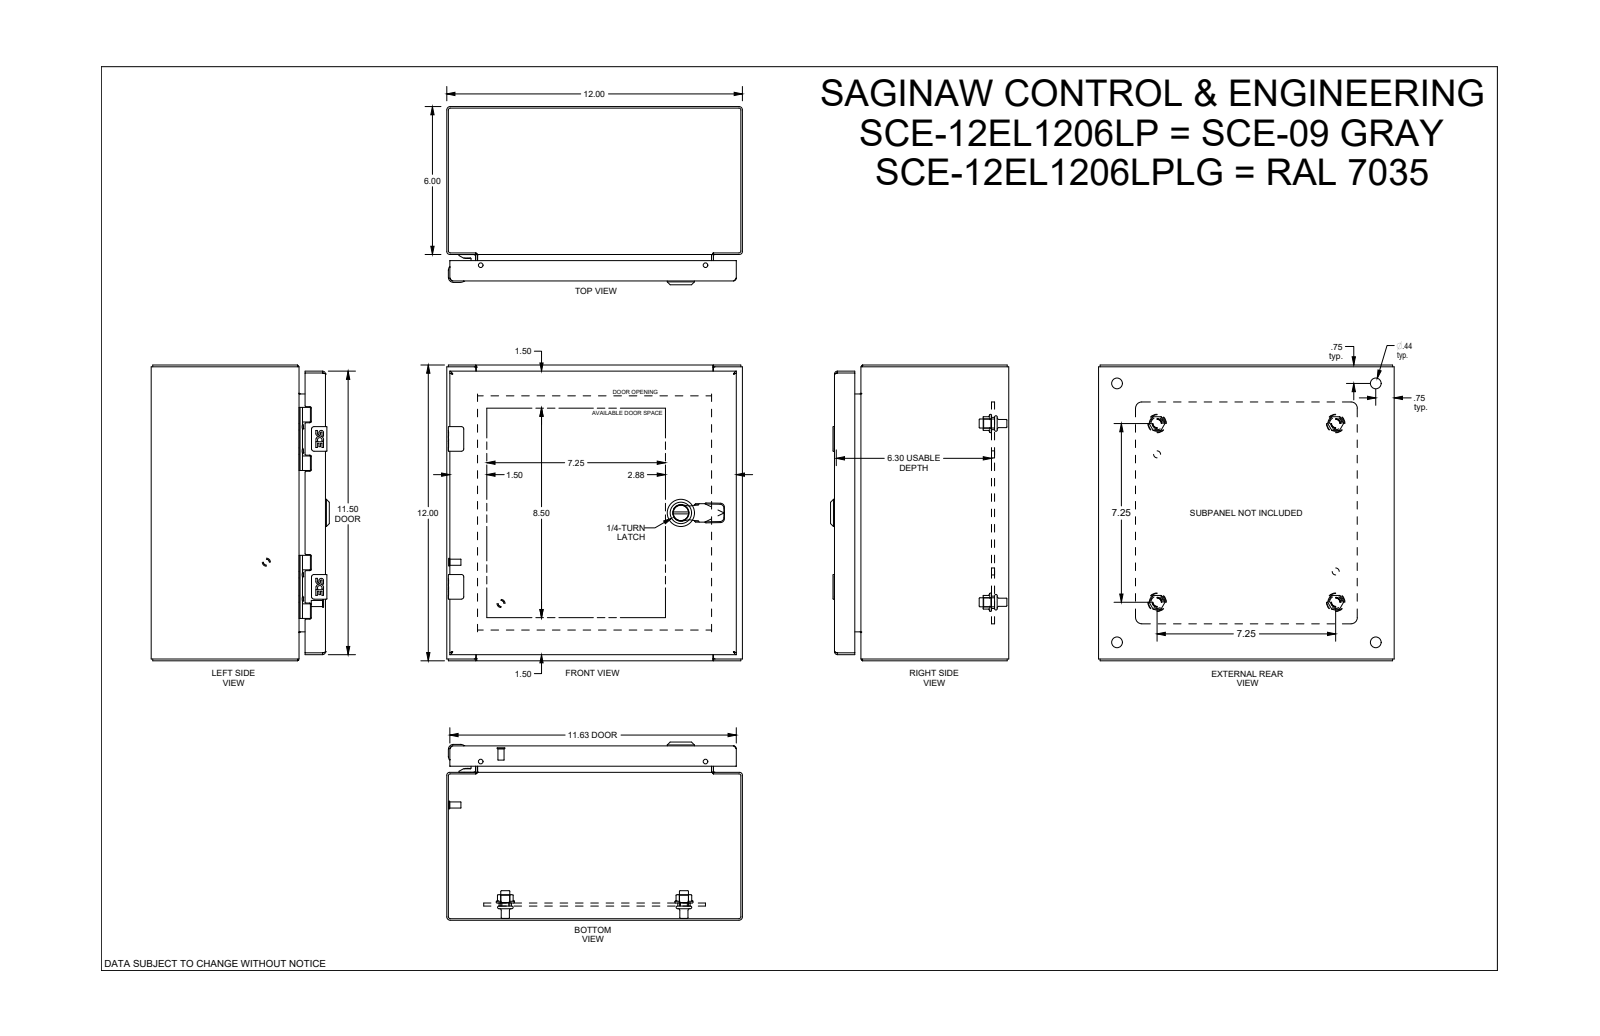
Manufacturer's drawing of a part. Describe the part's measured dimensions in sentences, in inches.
The part is named "SCE-12EL1206LP". Its 3-D file was written by "SolidWorks 2019 (AUTOMOTIVE_DESIGN)". It is 39 solids with 1793 faces: 856 planar, 561 cylindrical and 376 other. Overall it measures 12 by 12 by 7.23 inches. Its volume is 67.73 cubic inches and its surface area 1 657 square inches. Round holes: 4 of diameter 0.172, 4 of diameter 0.205, 4 of diameter 0.244, 4 of diameter 0.266, 4 of diameter 0.367, 4 of diameter 0.375, 4 of diameter 0.437, 4 of diameter 0.5, 2 of diameter 0.04, 2 of diameter 0.188, 2 of diameter 0.218, 2 of diameter 0.281. Round bosses or shafts: 6 of diameter 0.17, 4 of diameter 0.366, 4 of diameter 0.332, 4 of diameter 0.25, 4 of diameter 0.24, 3 of diameter 0.196, 2 of diameter 0.248, 1 of diameter 1.102. Partial cylindrical surfaces (rounded edges, fillets, slot ends): 30 of radius 0.012, 28 of radius 0.01, 24 of radius 0.015, 13 of radius 0.06, 12 of radius 0.02, 12 of radius 0.025, 12 of radius 0.1, 10 of radius 0.031. The main face-to-face distances are 0.075, 11.925, 0.06, 11.85, 12, 7.073, 6.998, 7.013, 6.938, 5.925. The hole center spacings are 9.022, 0.985, 6, 0.02, 0.493, 0.494, 2.298, 2.743.
